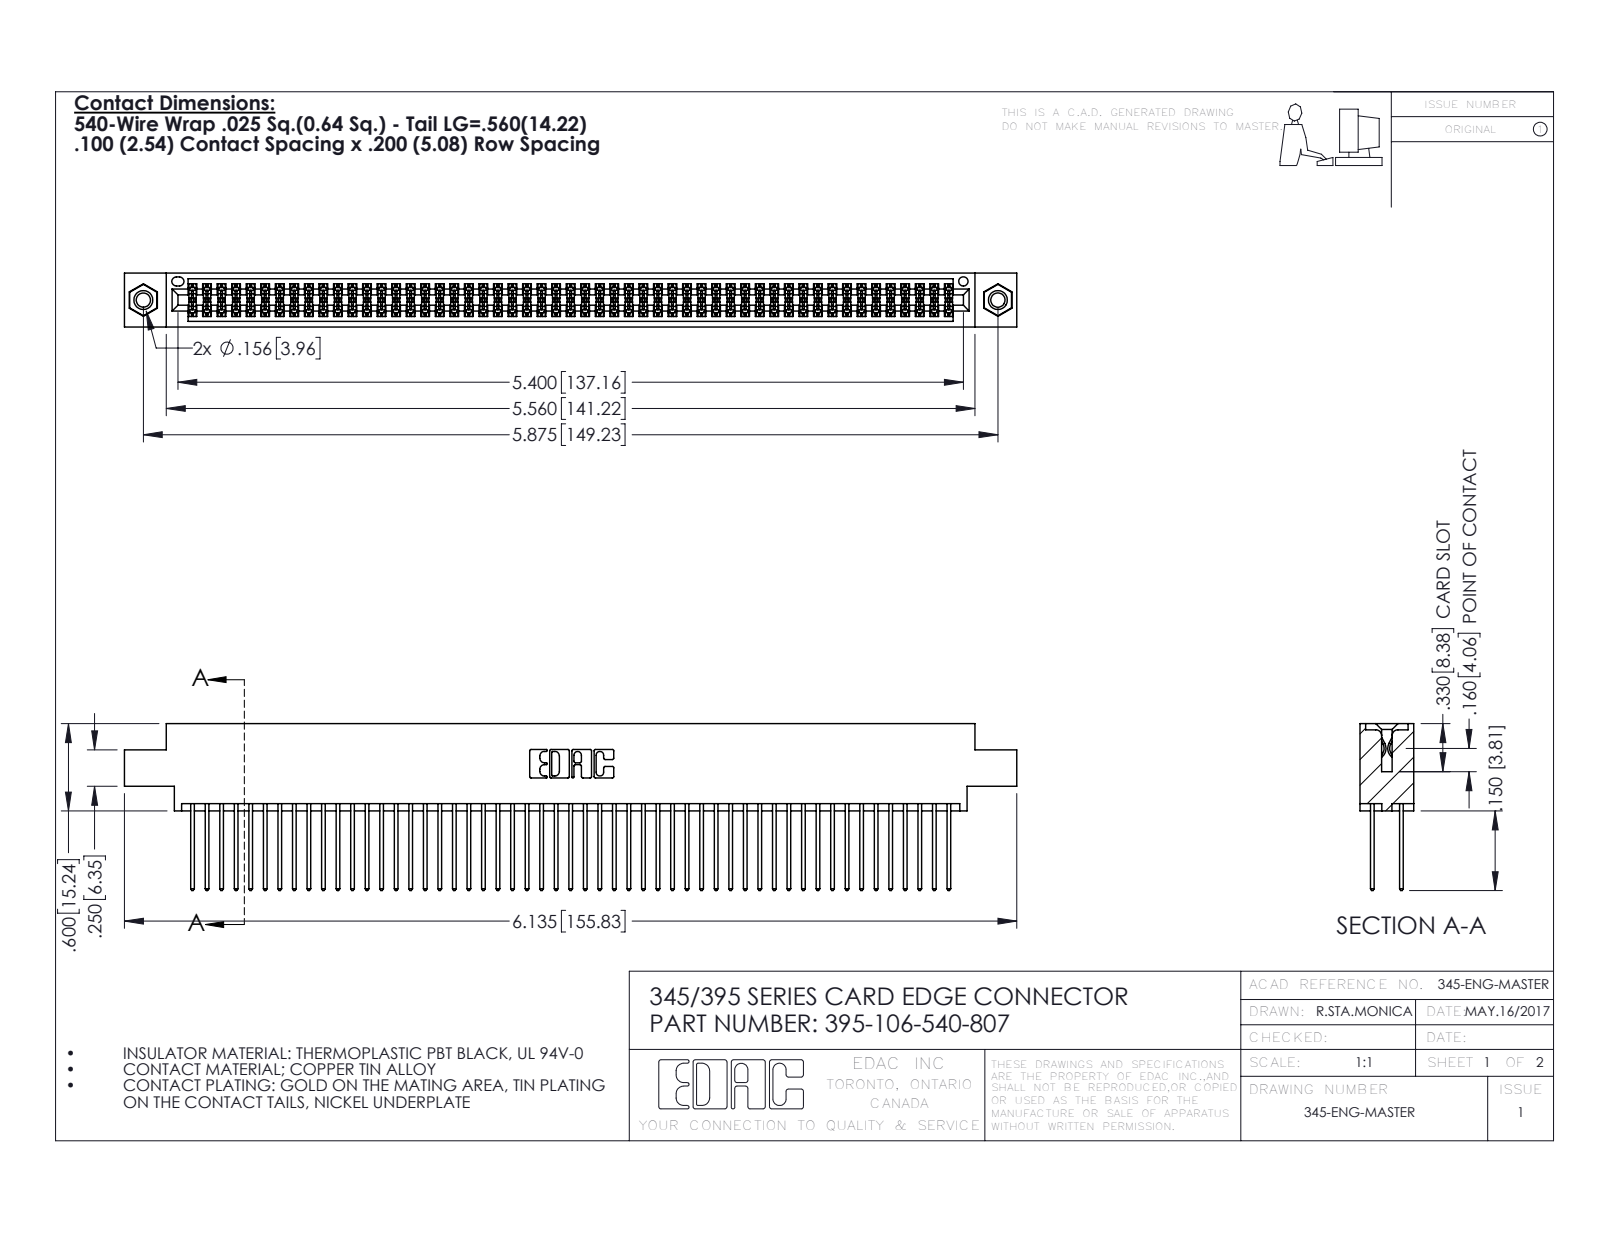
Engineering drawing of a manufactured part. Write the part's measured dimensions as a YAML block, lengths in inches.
part_name: "345-292-001_345-293-140; 345 Part_0.170 Offset - 0.156 Dia-TI; 395-106-540-807; 345-250-001_345-250-005-103"
step_written_by: "SolidWorks 2016 (CONFIG_CONTROL_DESIGN)"
units: inches
bodies: {solids: 109, faces: 5490, planar: 3614, cylindrical: 1860, other: 16}
overall_size: [6.135, 1.147, 0.37]
volume: 0.947
surface_area: 39.03
round_holes:
  - {diameter: 0.098, count: 2}
  - {diameter: 0.125, count: 2}
  - {diameter: 0.156, count: 2}
  - {diameter: 0.064, count: 1}
round_bosses_or_shafts:
  - {diameter: 0.155, count: 2}
partial_cylinders:
  - {radius: 0.006, count: 159}
  - {radius: 0.01, count: 106}
  - {radius: 0.01, count: 22}
  - {radius: 0.007, count: 6}
  - {radius: 0.031, count: 6}
  - {radius: 0.026, count: 3}
  - {radius: 0.014, count: 2}
  - {radius: 0.019, count: 2}
face_to_face_distances: [0.072, 0.298, 0.2, 0.098, 0.272, 0.025, 0.37, 0.225, 0.175, 0.149]
hole_center_spacings: [0.27, 5.639, 5.875]
